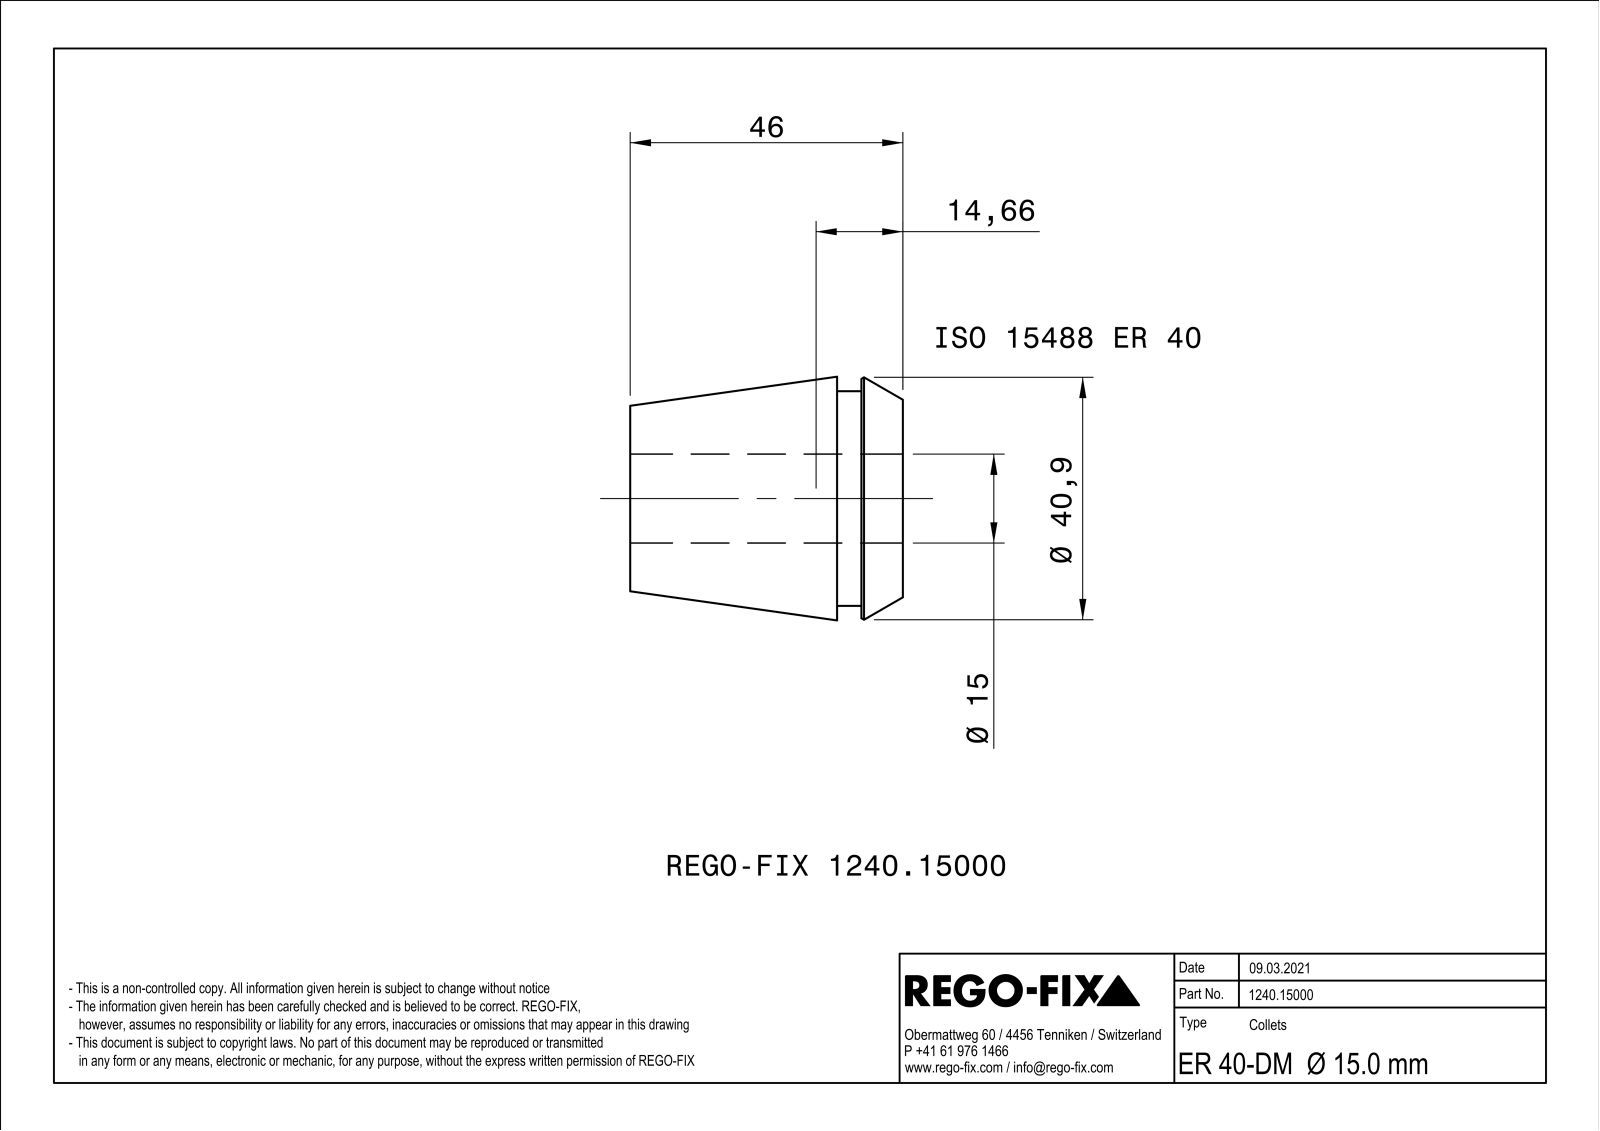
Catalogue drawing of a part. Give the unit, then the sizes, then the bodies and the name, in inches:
Units: inches
Overall size (bounding box): 1.811 × 1.614 × 1.614
Round holes (diameter × count): ⌀0.591 ×1
Round bosses / shafts (diameter × count): ⌀1.425 ×1
Main face-to-face distances: 0.039, 1.811, 0.437, 1.374, 0.276, 0.161, 1.535, 0.669, 0.394, 0.232
Volume: 2.061 in³ · Surface area: 31.15 in²
Bodies: 1 solid, 154 faces (80 planar, 9 cylindrical, 65 other)
Part name (STEP PRODUCT): NOCUT
STEP written by: SIEMENS PLM Software Solid Edge ST10 (AUTOMOTIVE_DESIGN)
